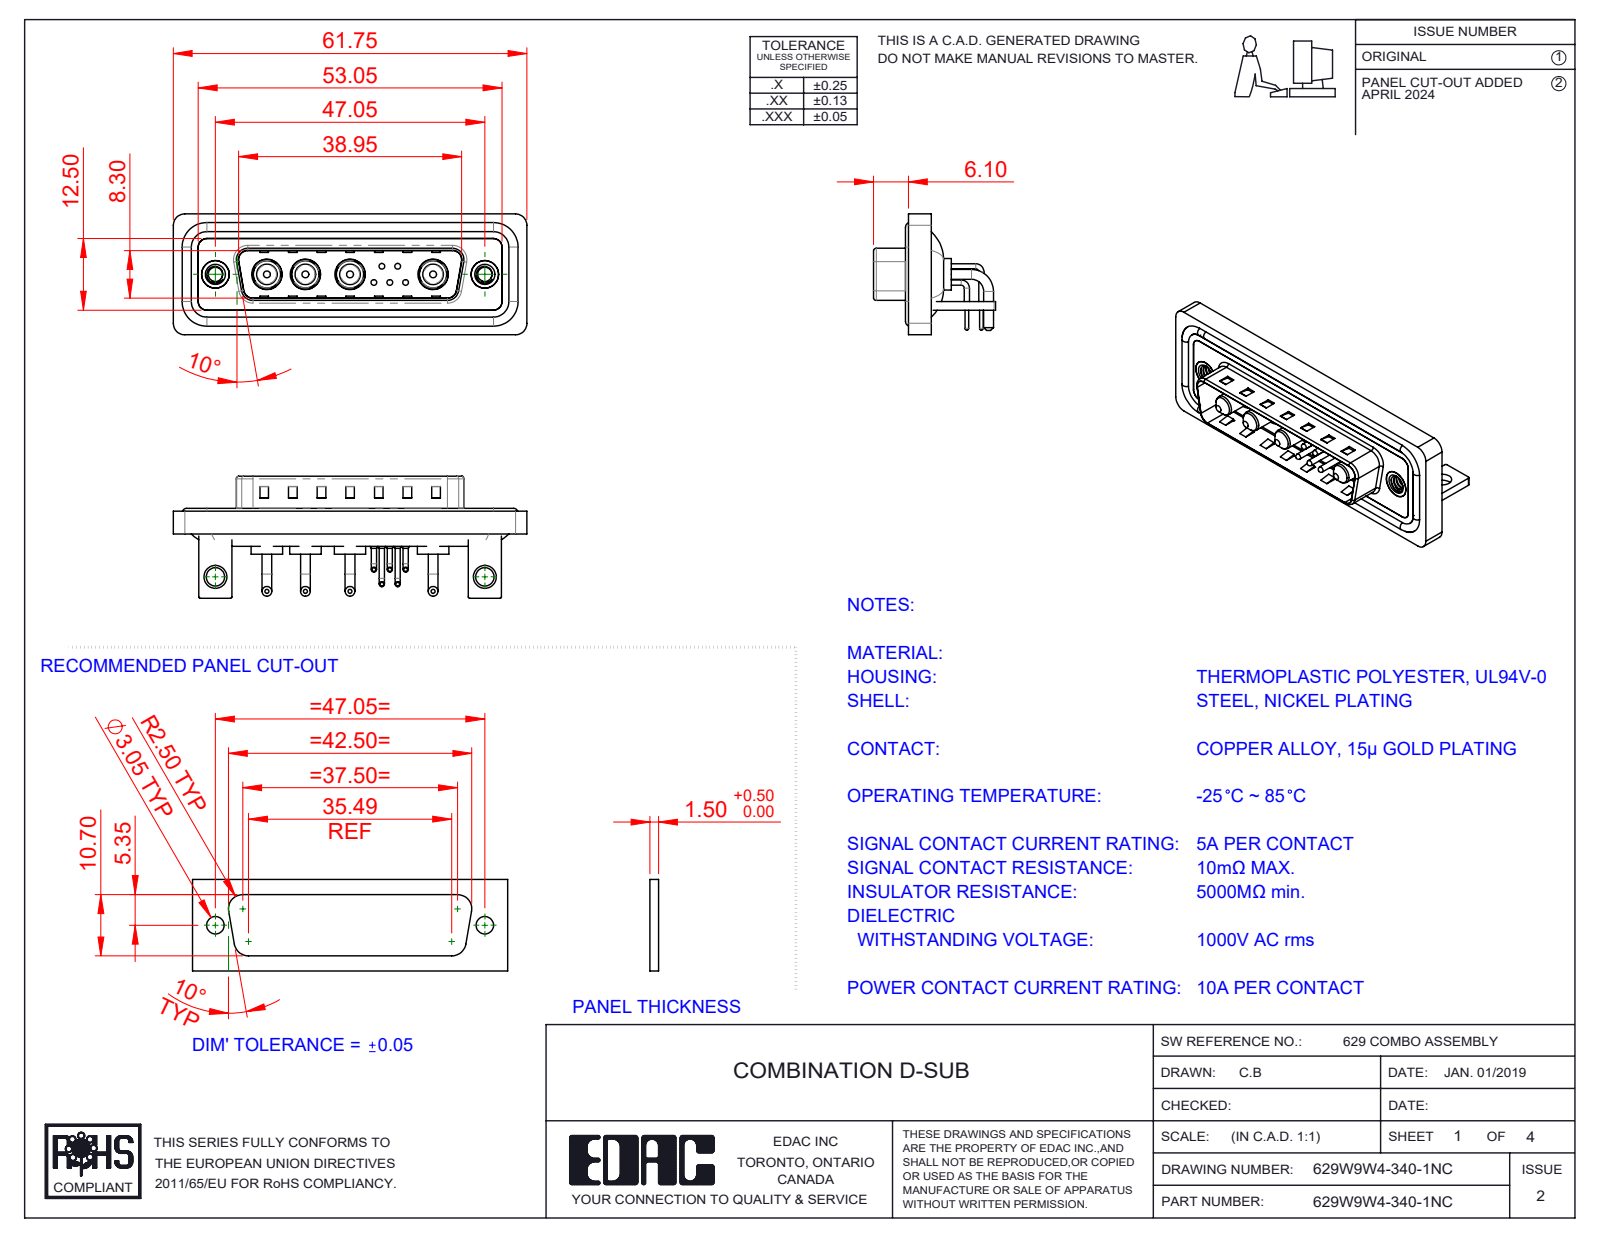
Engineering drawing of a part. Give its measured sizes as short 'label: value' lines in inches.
name: 629Combo Stabilizer Bracket; 629Combo Contact Row 1; 629Combo Shell Rear_25 Contacts; 629Combo Threaded Rivet_B (+6 more)
written by: SolidWorks 2023 (CONFIG_CONTROL_DESIGN)
unit: in
bodies: 22 solids, 1243 faces (589 planar, 470 cylindrical, 184 other)
size: 2.431 × 0.839 × 0.831
volume: 0.473 in³; area: 19.78 in²
holes: 5× ⌀0.03, 5× ⌀0.063, 5× ⌀0.079, 4× ⌀0.191, 4× ⌀0.209, 2× ⌀0.098, 2× ⌀0.126, 2× ⌀0.157, 2× ⌀0.189, 2× ⌀0.197
bosses: 10× ⌀0.035, 8× ⌀0.067, 5× ⌀0.059, 5× ⌀0.039, 5× ⌀0.026, 4× ⌀0.217, 4× ⌀0.205, 4× ⌀0.187
rounds: 19× R0.079, 18× R0.059, 16× R0.01, 9× R0.02, 8× R0.063, 5× R0.04, 4× R0.024, 4× R0.026
face distances: 0.016, 0.059, 0.031, 0.114, 0.083, 0.043, 0.146, 0.161, 0.177, 0.063
hole spacings: 0.124, 0.109, 0.198, 0.571, 1.852, 0.109, 0.173, 0.174
